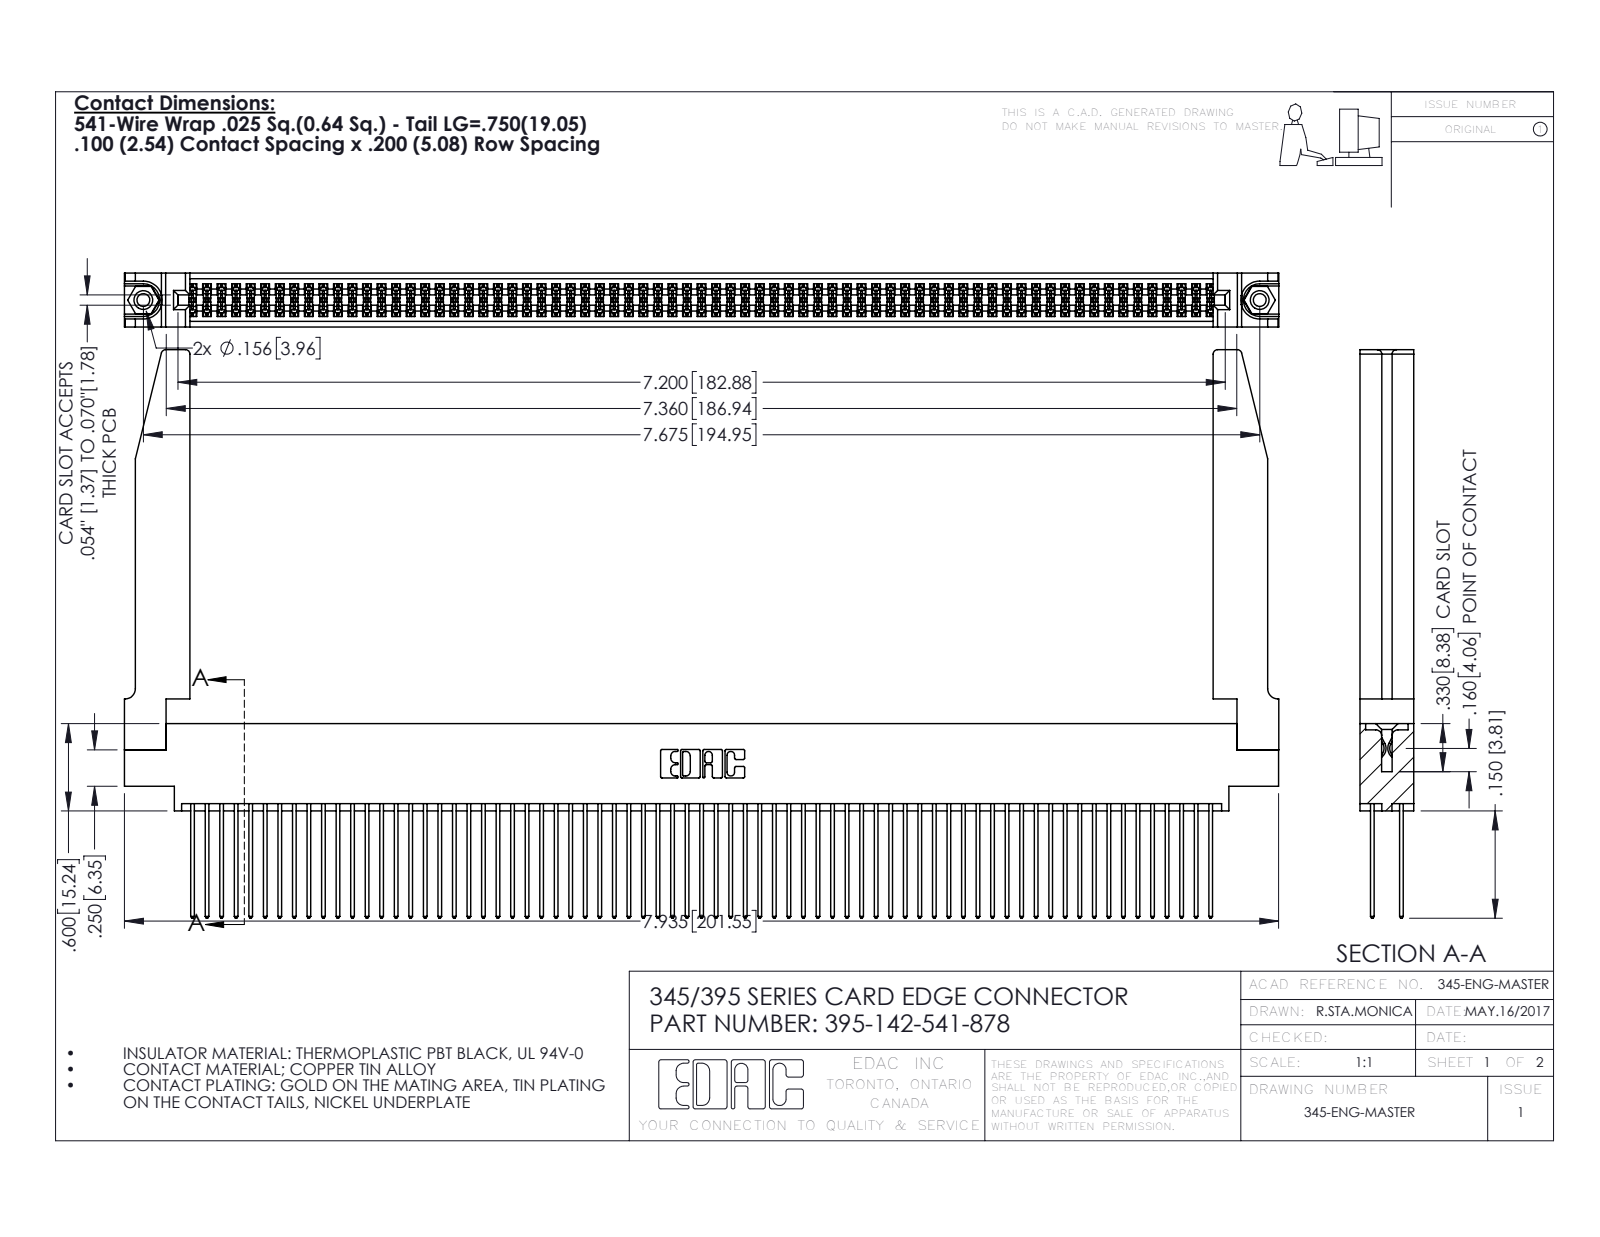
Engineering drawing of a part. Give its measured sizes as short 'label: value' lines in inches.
name: 345-292-001_345-293-141; 345-220-078_345-220-078; 345 Part_0.170 Offset - 0.156 Dia-TH; 345-250-001_345-250-001-102 (+1 more)
written by: SolidWorks 2016 (CONFIG_CONTROL_DESIGN)
unit: in
bodies: 147 solids, 7464 faces (4912 planar, 2500 cylindrical, 52 other)
size: 7.936 × 3.907 × 0.37
volume: 1.728 in³; area: 64.72 in²
holes: 2× ⌀0.089, 2× ⌀0.125, 2× ⌀0.156, 1× ⌀0.064
bosses: 2× ⌀0.155
rounds: 213× R0.006, 142× R0.01, 22× R0.01, 8× R0.03, 6× R0.007, 6× R0.031, 3× R0.026, 2× R0.014
face distances: 0.072, 0.298, 0.098, 0.272, 0.025, 0.2, 0.37, 0.225, 0.175, 0.149
hole spacings: 0.27, 7.439, 7.675
